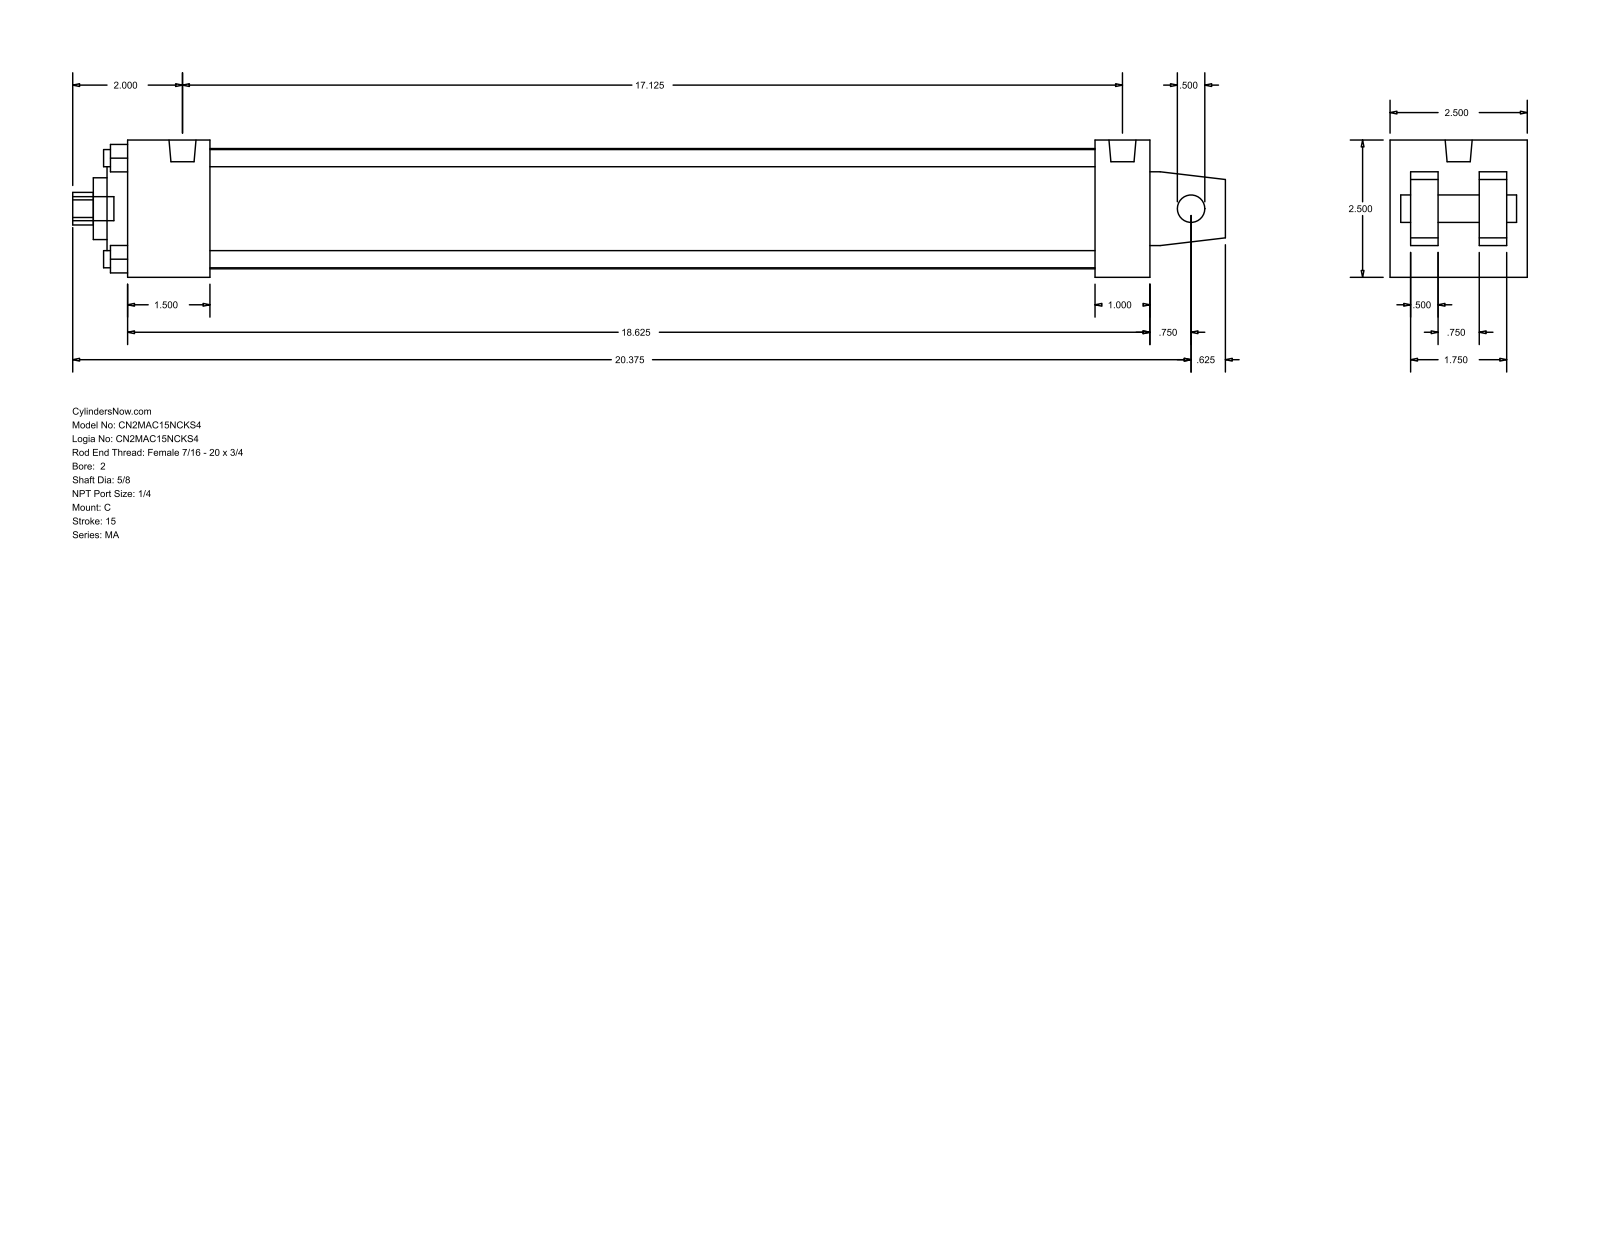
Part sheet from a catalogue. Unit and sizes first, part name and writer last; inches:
Units: inches
Overall size (bounding box): 21 × 2.5 × 2.5
Round holes (diameter × count): ⌀0.313 ×4, ⌀0.5 ×1, ⌀0.625 ×1, ⌀1.125 ×1, ⌀2 ×1, ⌀2.19 ×1
Round bosses / shafts (diameter × count): ⌀0.313 ×4, ⌀0.492 ×2, ⌀0.437 ×1
Partial cylindrical surfaces — rounded edges, fillets, slot ends (radius × count): R0.297 ×1
Main face-to-face distances: 2.5, 0.375, 0.5, 0.875, 1.625, 2.125, 1.25, 1.5, 18.625, 17.125
Hole centre spacings: 1.301, 1.84, 2.602
Bodies: 0 solids, 105 faces (77 planar, 28 cylindrical, 0 other)
Part name (STEP PRODUCT): MA_C__0200_0.625
STEP written by: GSSL Pune (CONFIG_CONTROL_DESIGN)
